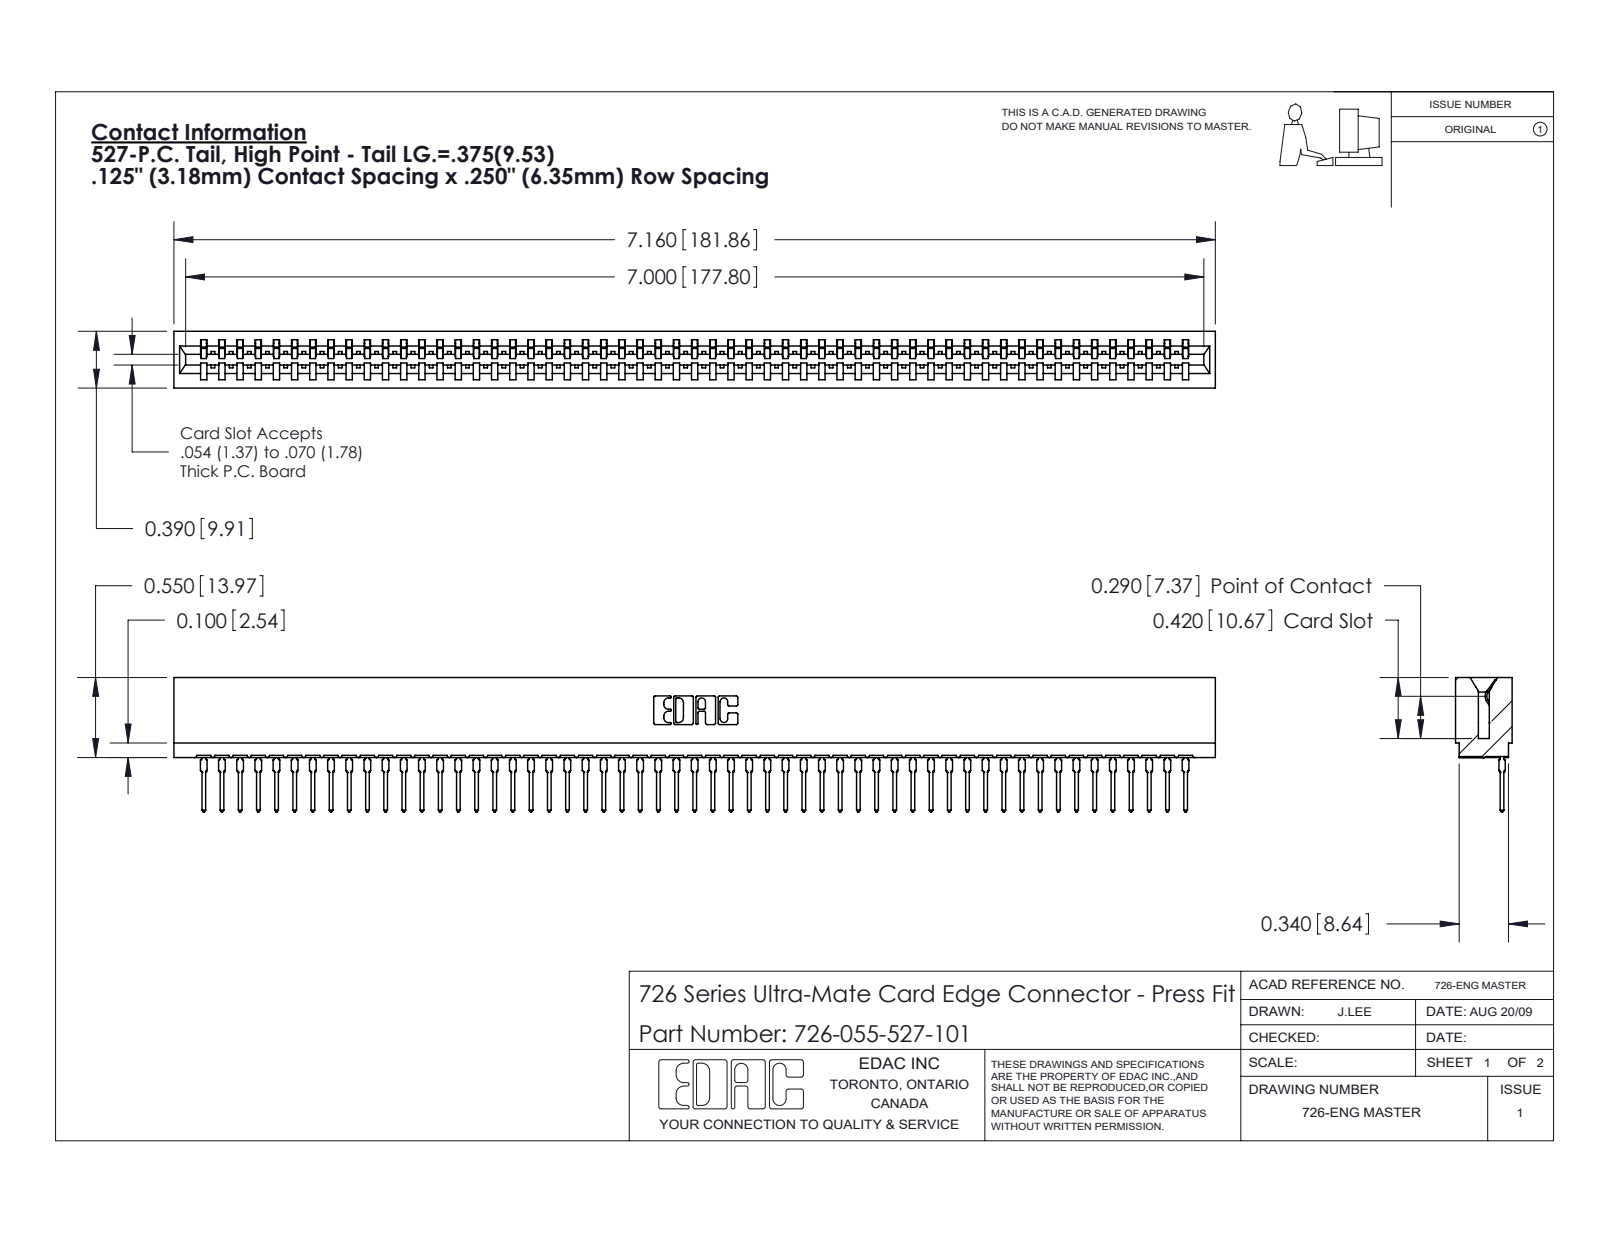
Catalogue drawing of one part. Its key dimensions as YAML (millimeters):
part_name: "726 Part_.515 Slot Depth - 01; 746-292-001_527; 726-055-527-101"
step_written_by: "SolidWorks 2020 (CONFIG_CONTROL_DESIGN)"
units: millimeters
bodies: {solids: 56, faces: 6037, planar: 3520, cylindrical: 1087, other: 1430}
overall_size: [181.9, 23.5, 9.9]
volume: 16200
surface_area: 25250
partial_cylinders:
  - {radius: 0.5, count: 110}
  - {radius: 0.4, count: 56}
  - {radius: 0.3, count: 22}
  - {radius: 0.2, count: 6}
  - {radius: 0.8, count: 6}
  - {radius: 0.1, count: 4}
  - {radius: 0.3, count: 4}
  - {radius: 0.7, count: 3}
face_to_face_distances: [1.4, 8.5, 9.9, 0.6, 7.8, 6.4, 7, 2.1, 9.3, 0.8]
